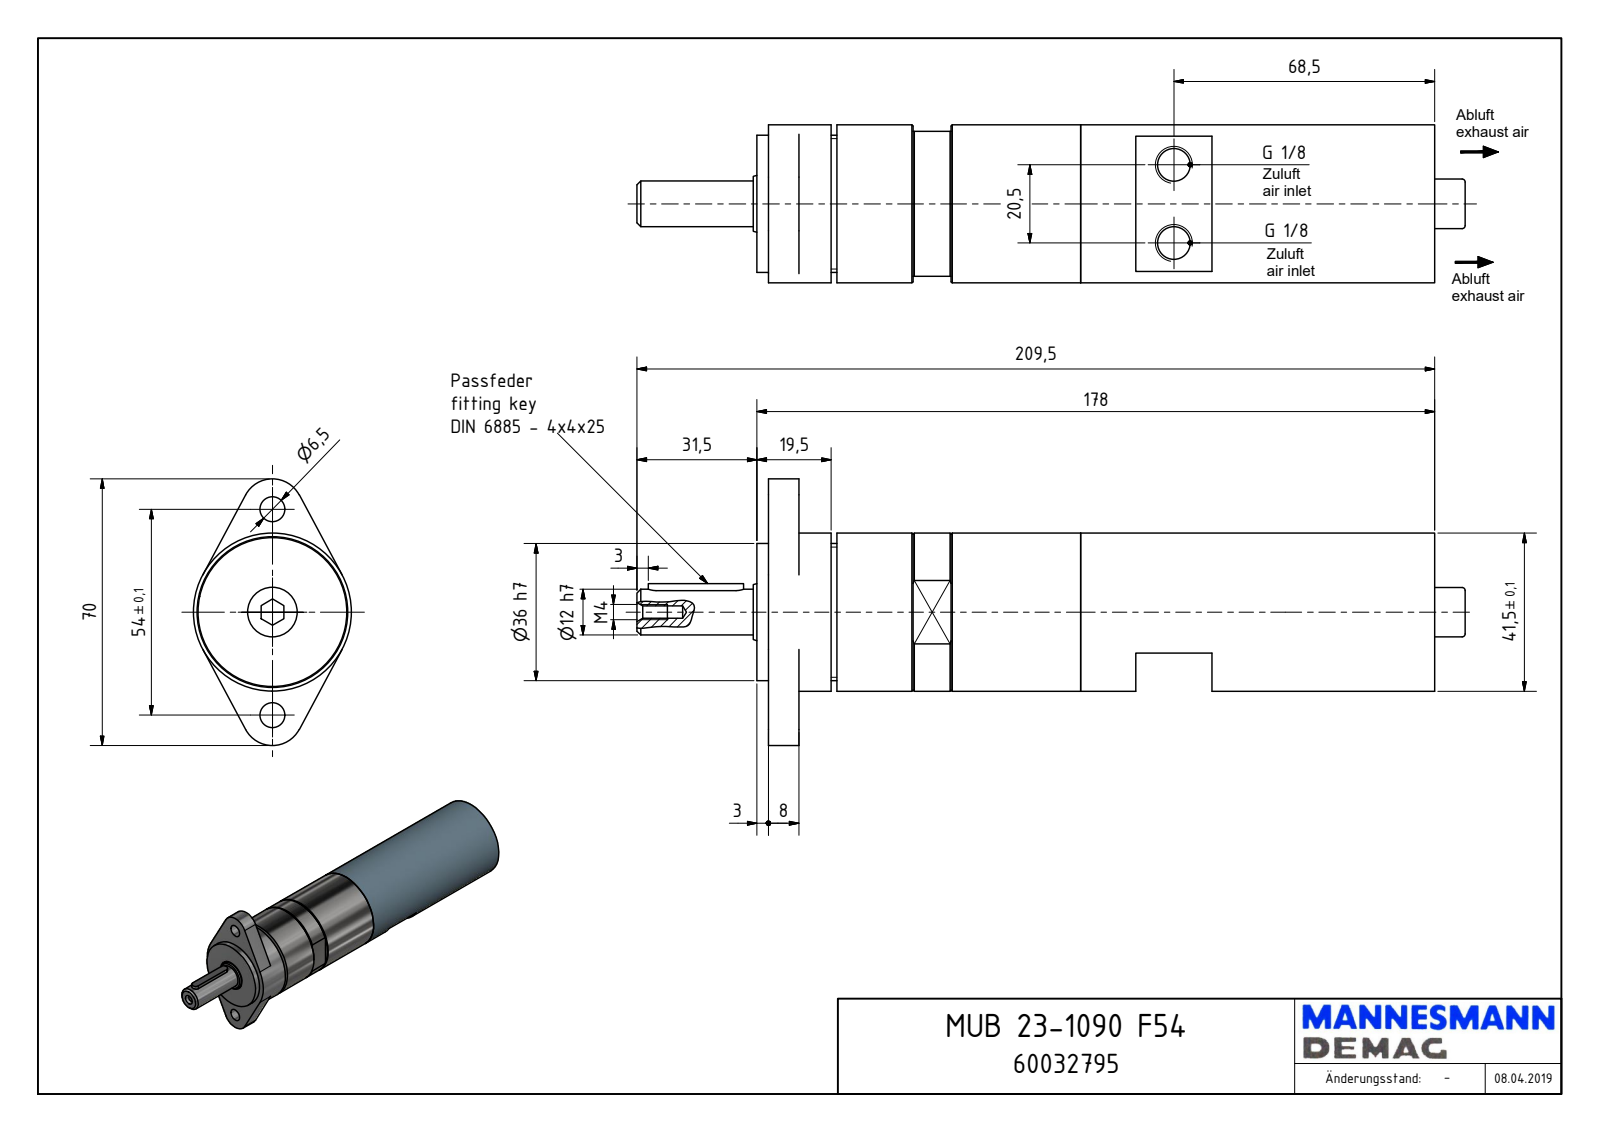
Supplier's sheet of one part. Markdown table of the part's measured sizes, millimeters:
| quantity | value |
| --- | --- |
| part name | MUB 23-1090 F54_60032795 |
| STEP written by | Autodesk Inventor 2018 (AUTOMOTIVE_DESIGN) |
| units | millimeters |
| bodies | 1 solid, 128 faces (63 planar, 49 cylindrical, 16 other) |
| overall size | 217.5 × 70 × 41.5 |
| volume | 239 634 mm³ |
| surface area | 35 778 mm² |
| round holes (diameter × count) | 2 × 2, 6.5 × 2, 8.57 × 2, 3.24 × 1, 8.5 × 1, 13 × 1, 16 × 1, 37 × 1, 38.01 × 1, 39.5 × 1 |
| round bosses / shafts (diameter × count) | 41.5 × 1, 39 × 1, 36 × 1, 14.95 × 1, 12 × 1, 8 × 1 |
| partial cylindrical surfaces (radius × count) | 2 × 4, 2.5 × 2, 8 × 2, 8.1 × 1, 12.51 × 1, 20.12 × 1 |
| main face-to-face distances | 175, 3, 178, 95.6, 92.6, 82.4, 96, 93, 0.4, 82 |
| hole center spacings | 12.94, 26.75, 27, 32.82, 20.5, 25, 54 |
